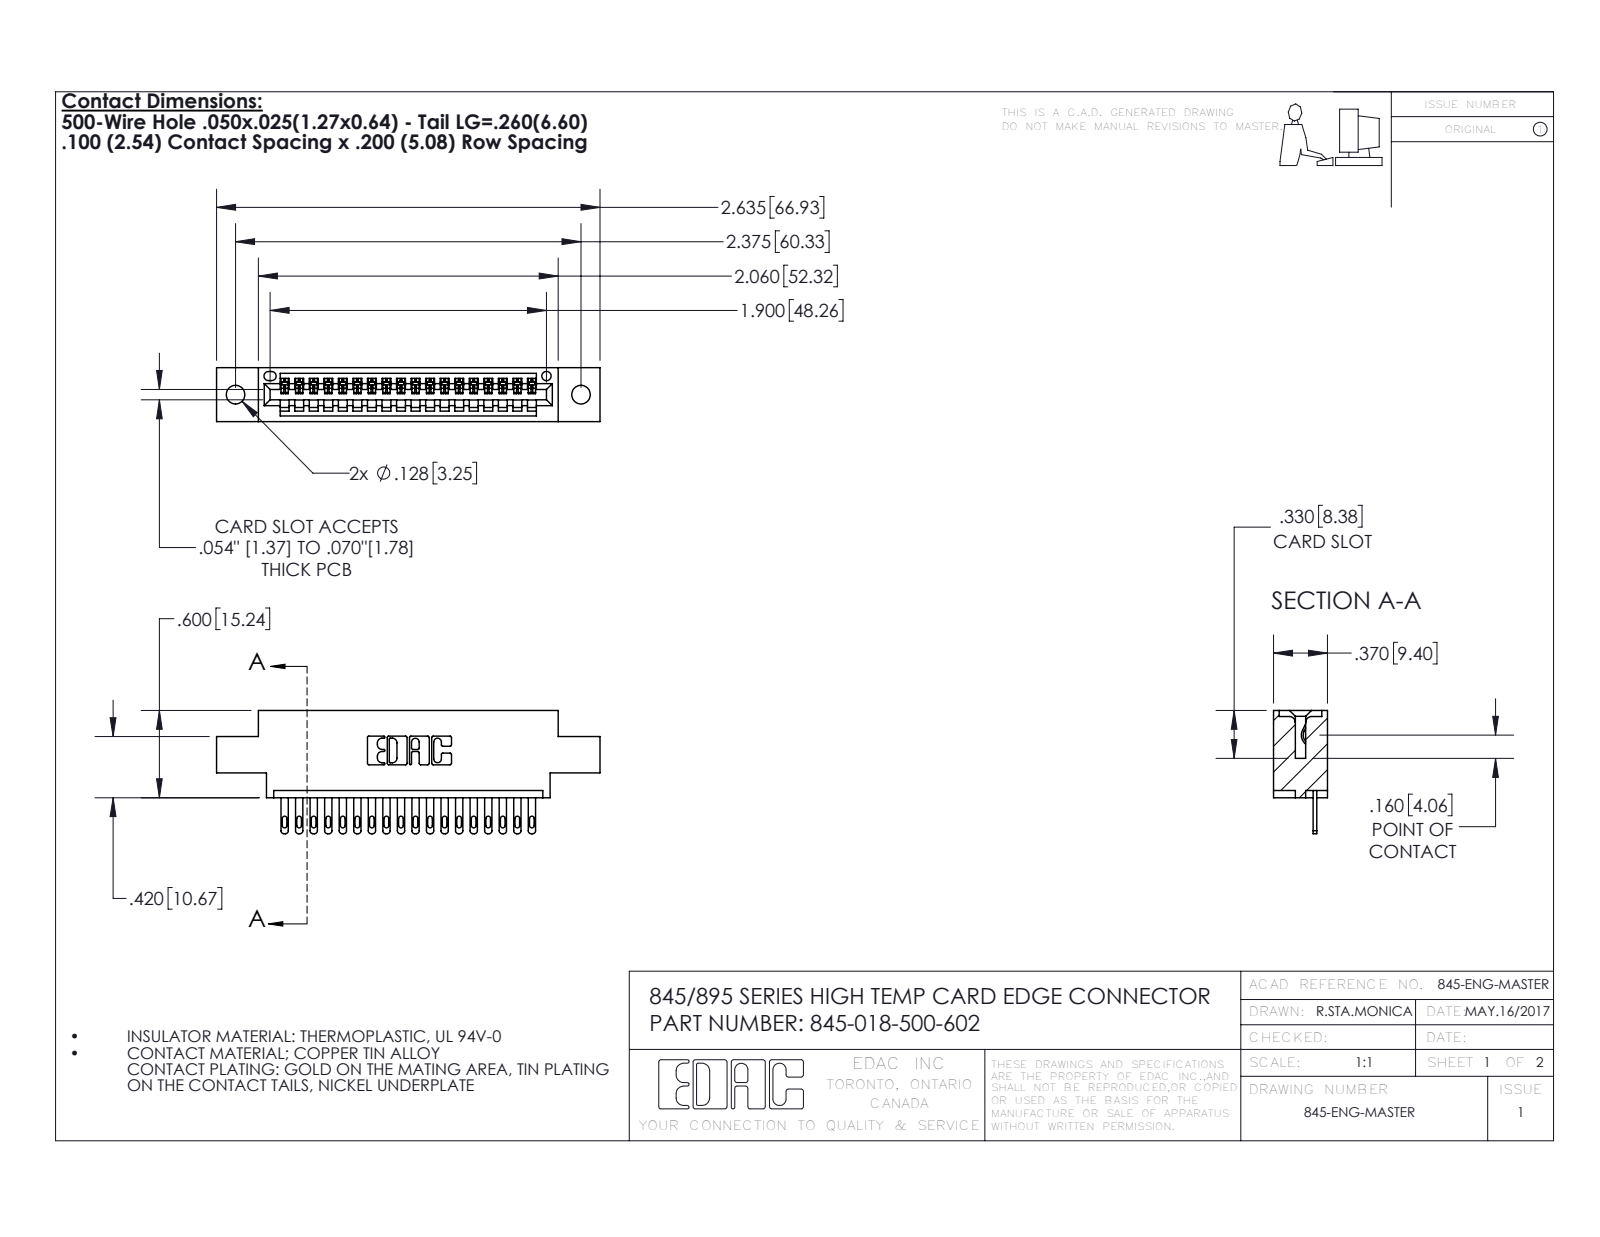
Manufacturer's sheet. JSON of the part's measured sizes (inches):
{"part_name": "345 Part_0.170 Offset - 0.128 Dia; 345-018-500-602; 345-292-001_345-293-100", "step_written_by": "SolidWorks 2016 (CONFIG_CONTROL_DESIGN)", "units": "inches", "bodies": {"solids": 19, "faces": 1103, "planar": 697, "cylindrical": 406, "other": 0}, "overall_size": [2.635, 0.847, 0.37], "volume_in3": 0.355, "surface_area_in2": 11.54, "round_holes": [[0.128, 2], [0.064, 1]], "partial_cylinders_radius": [[0.006, 36], [0.016, 36], [0.02, 36], [0.01, 22], [0.007, 6], [0.031, 6], [0.026, 3], [0.031, 2]], "face_to_face_distances": [0.298, 0.072, 0.37, 0.2, 0.098, 0.272, 0.025, 0.225, 0.15, 0.1], "hole_center_spacings": [0.27, 2.141, 2.375]}
